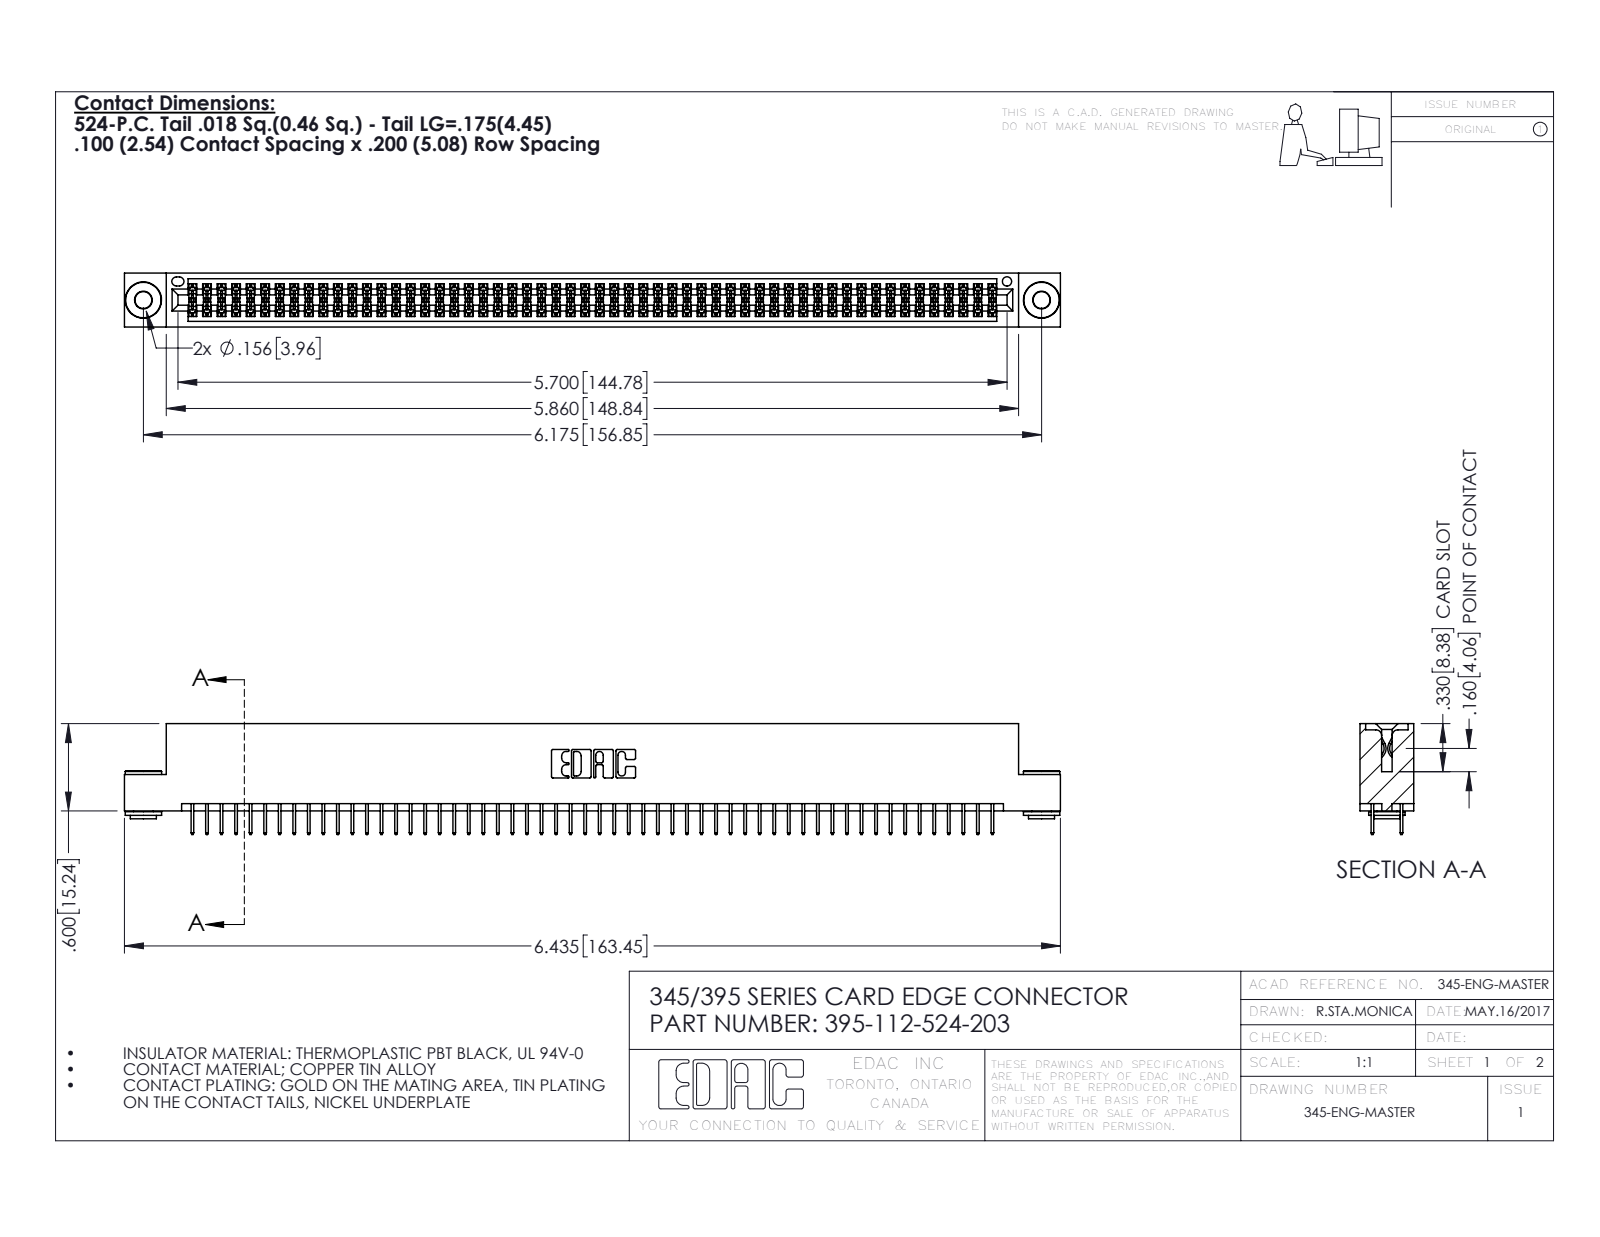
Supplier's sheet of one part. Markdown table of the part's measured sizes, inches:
| quantity | value |
| --- | --- |
| part name | 395-112-524-203; 345-292-001_345-293-124; 345 Part_Flush Mounting Lugs - 0.156 Dia-TH; 345-250-002_345-250-002-102 |
| STEP written by | SolidWorks 2016 (CONFIG_CONTROL_DESIGN) |
| units | inches |
| bodies | 115 solids, 6212 faces (4458 planar, 1746 cylindrical, 8 other) |
| overall size | 6.435 × 0.762 × 0.37 |
| volume | 0.968 in³ |
| surface area | 36.38 in² |
| round holes (diameter × count) | 0.116 × 2, 0.156 × 2, 0.064 × 1 |
| round bosses / shafts (diameter × count) | 0.25 × 2, 0.18 × 2, 0.136 × 2 |
| partial cylindrical surfaces (radius × count) | 0.006 × 168, 0.01 × 22, 0.007 × 6, 0.031 × 6, 0.026 × 3, 0.014 × 2, 0.019 × 2, 0.022 × 2 |
| main face-to-face distances | 0.072, 0.298, 0.2, 0.37, 0.025, 0.098, 0.272, 0.225, 0.072, 0.175 |
| hole center spacings | 0.27, 5.939, 6.175 |
